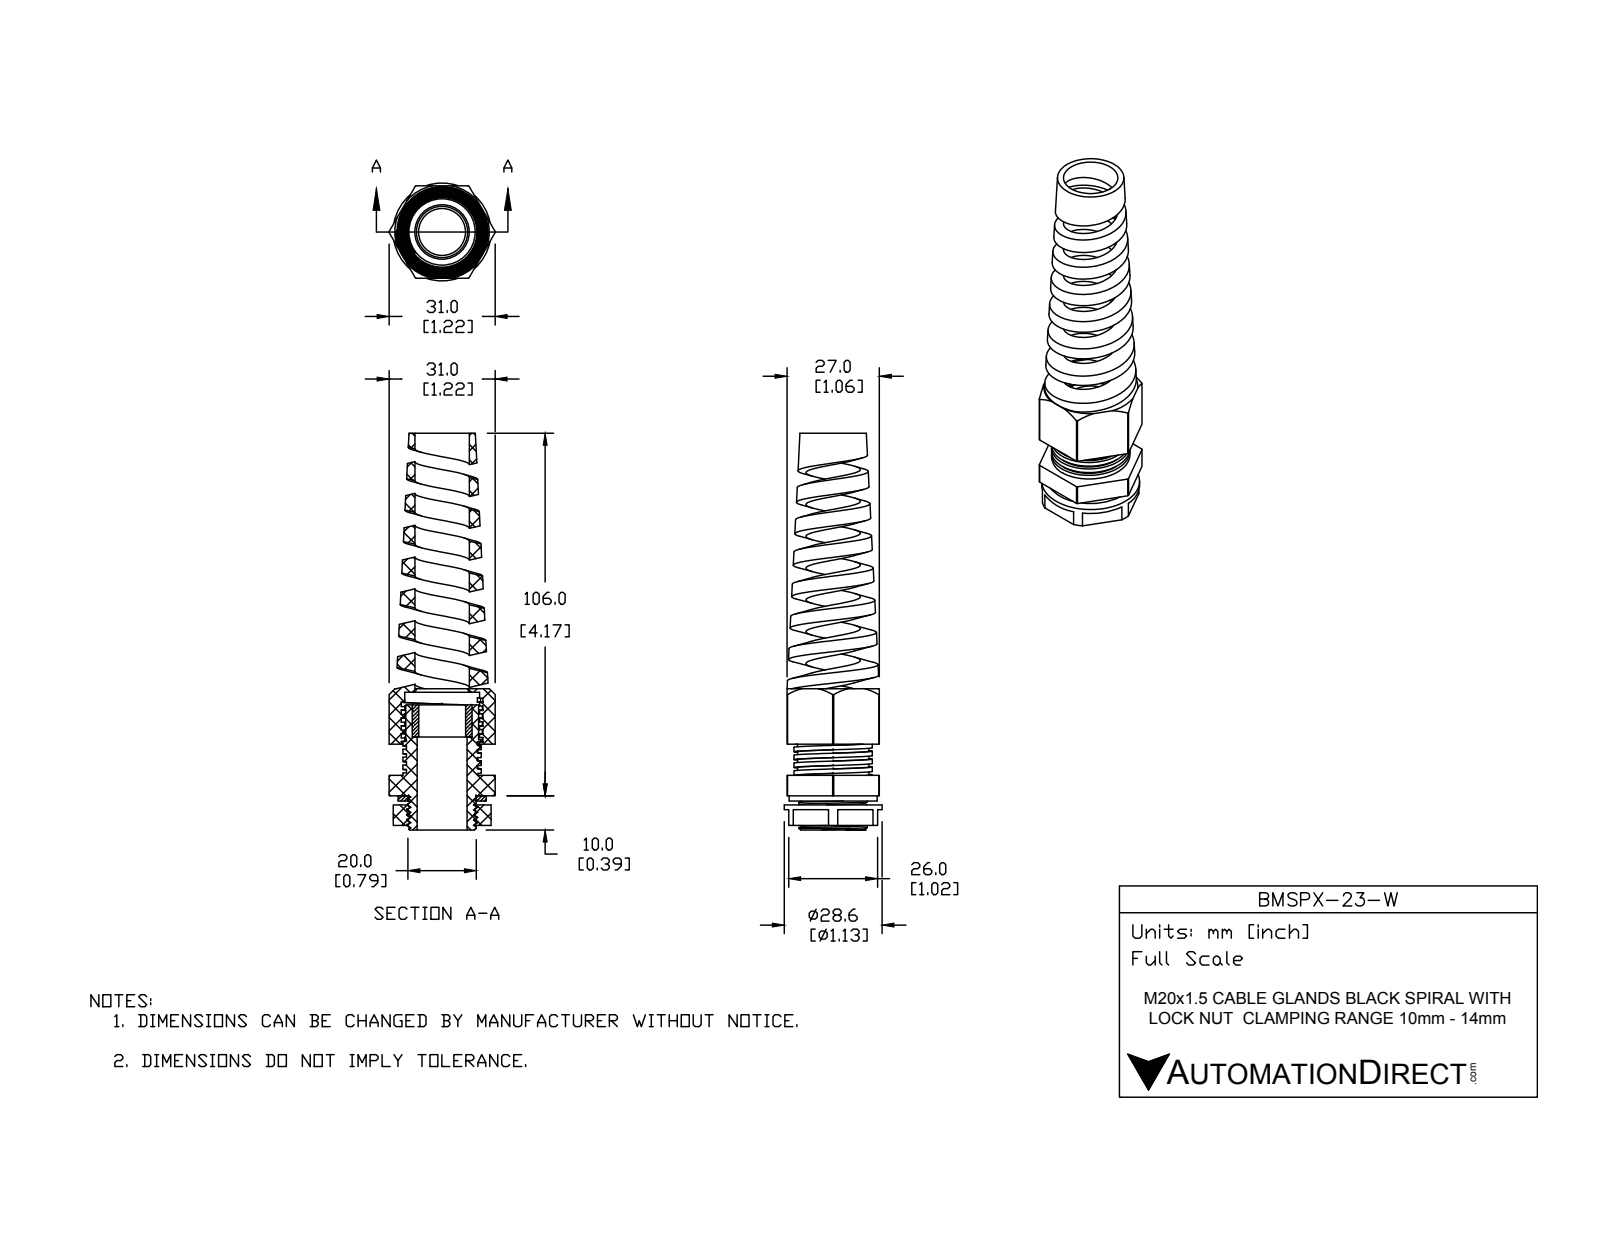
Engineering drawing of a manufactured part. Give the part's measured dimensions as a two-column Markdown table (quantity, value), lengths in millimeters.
| quantity | value |
| --- | --- |
| part name | BMSPX-23-W |
| STEP written by | SolidWorks 2015 (CONFIG_CONTROL_DESIGN) |
| units | millimeters |
| bodies | 5 solids, 240 faces (104 planar, 95 cylindrical, 41 other) |
| overall size | 116 × 31 × 28.6 |
| volume | 22 678 mm³ |
| surface area | 22 864 mm² |
| round holes (diameter × count) | 13.7 × 1, 14.6 × 1, 15.9 × 1, 17.5 × 1, 19.18 × 1, 19.8 × 1, 21.9 × 1 |
| round bosses / shafts (diameter × count) | 28.6 × 1, 25.75 × 1, 22.9 × 1, 21.3 × 1, 20 × 1 |
| partial cylindrical surfaces (radius × count) | 15.5 × 1 |
| main face-to-face distances | 27, 8.5, 0.5, 6, 1, 32.8, 2.5, 26.5, 1.5, 7.5 |
